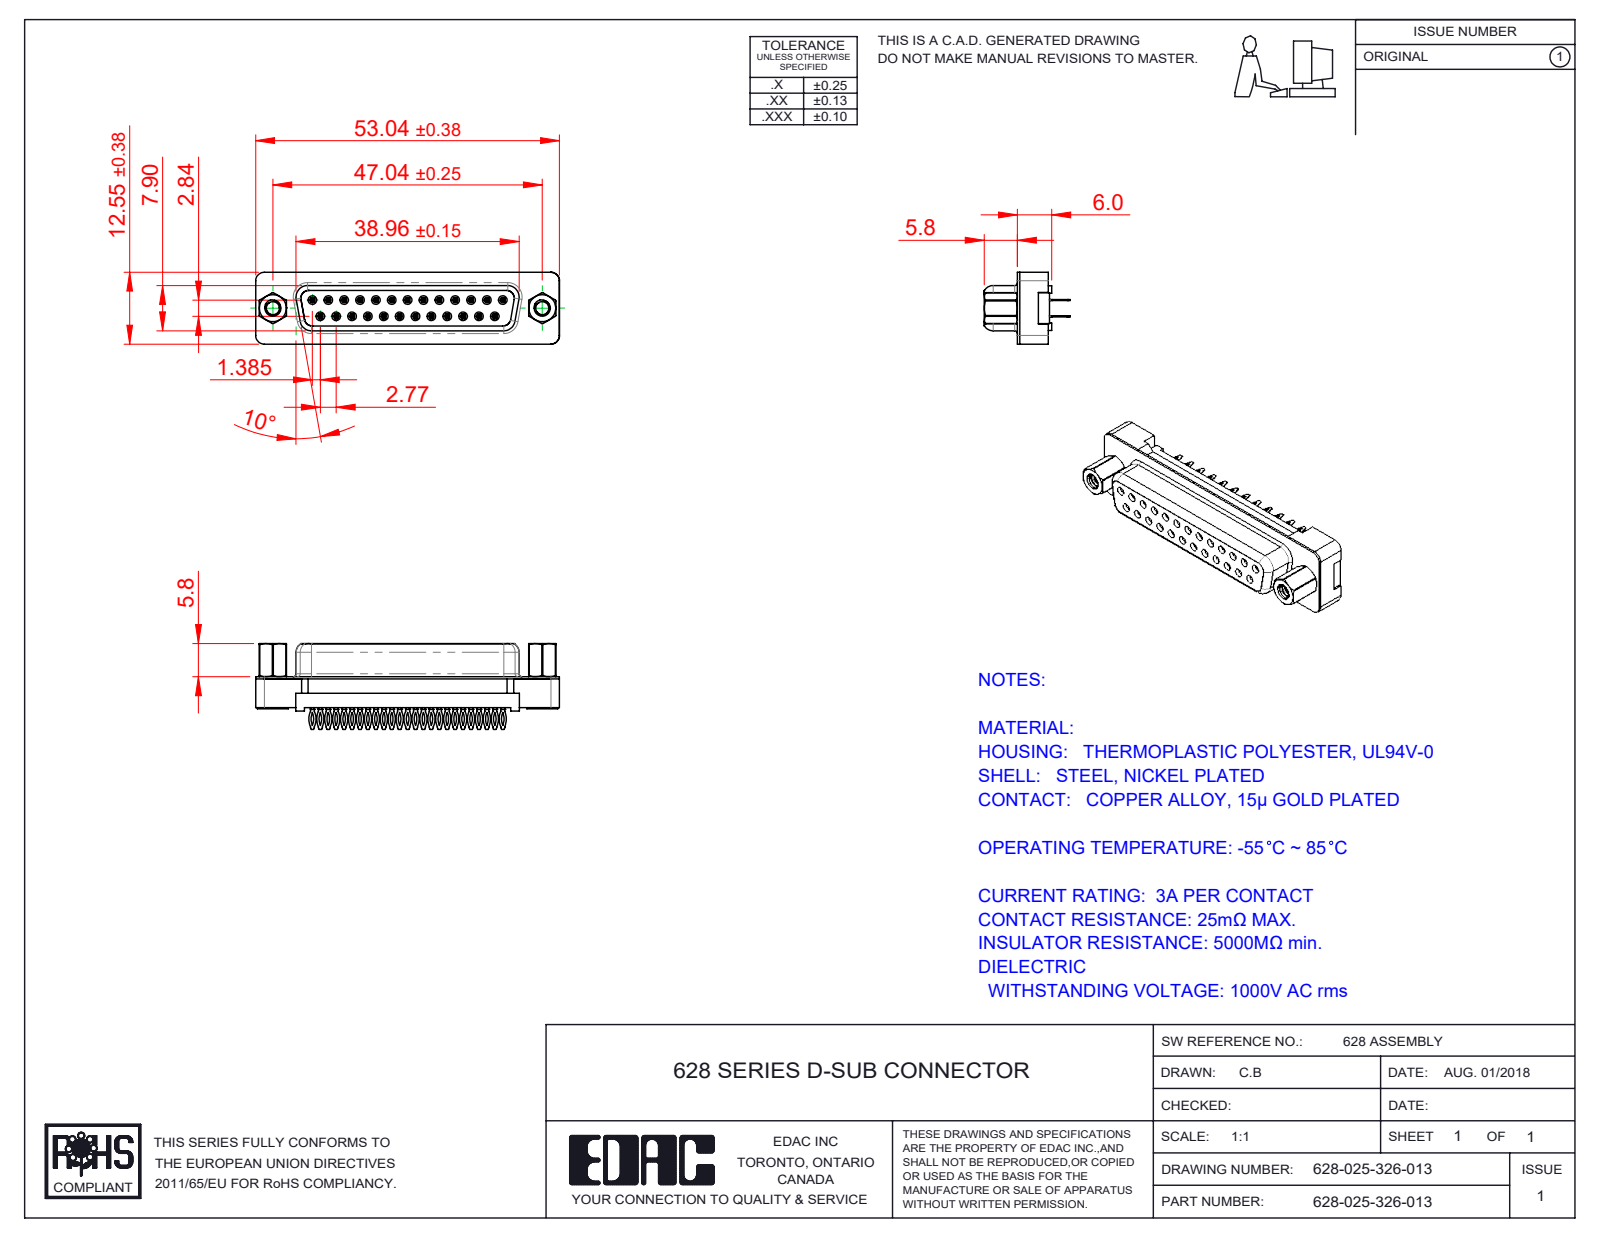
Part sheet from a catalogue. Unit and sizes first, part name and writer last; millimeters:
Units: millimetres
Overall size (bounding box): 53.05 × 15 × 12.55
Round holes (diameter × count): ⌀0.9 ×25, ⌀2.26 ×2, ⌀2.29 ×2, ⌀3.05 ×2, ⌀4 ×2, ⌀4.8 ×2, ⌀5 ×2
Round bosses / shafts (diameter × count): ⌀4.9 ×2, ⌀2.79 ×2
Partial cylindrical surfaces — rounded edges, fillets, slot ends (radius × count): R0.25 ×100, R2.92 ×50, R3.33 ×50, R0.5 ×29, R0.3 ×25, R1.35 ×9, R1.5 ×5, R0.9 ×4
Main face-to-face distances: 0.4, 2.84, 6.2, 2.5, 0.68, 5.52, 2.68, 3.52, 2, 5.54
Hole centre spacings: 3.16, 2.77, 5.54, 8.31, 11.08, 13.85, 5.04, 7.49
Volume: 3 499 mm³ · Surface area: 8 970 mm²
Bodies: 31 solids, 2621 faces (1046 planar, 676 cylindrical, 899 other)
Part name (STEP PRODUCT): 628 PB 4-40 Threaded Rivet; 628 PB Shell_25 Contacts; 628 PB Contact Row 2_26; 628 PB Contact Row 1_26 (+3 more)
STEP written by: SolidWorks 2020 (CONFIG_CONTROL_DESIGN)
